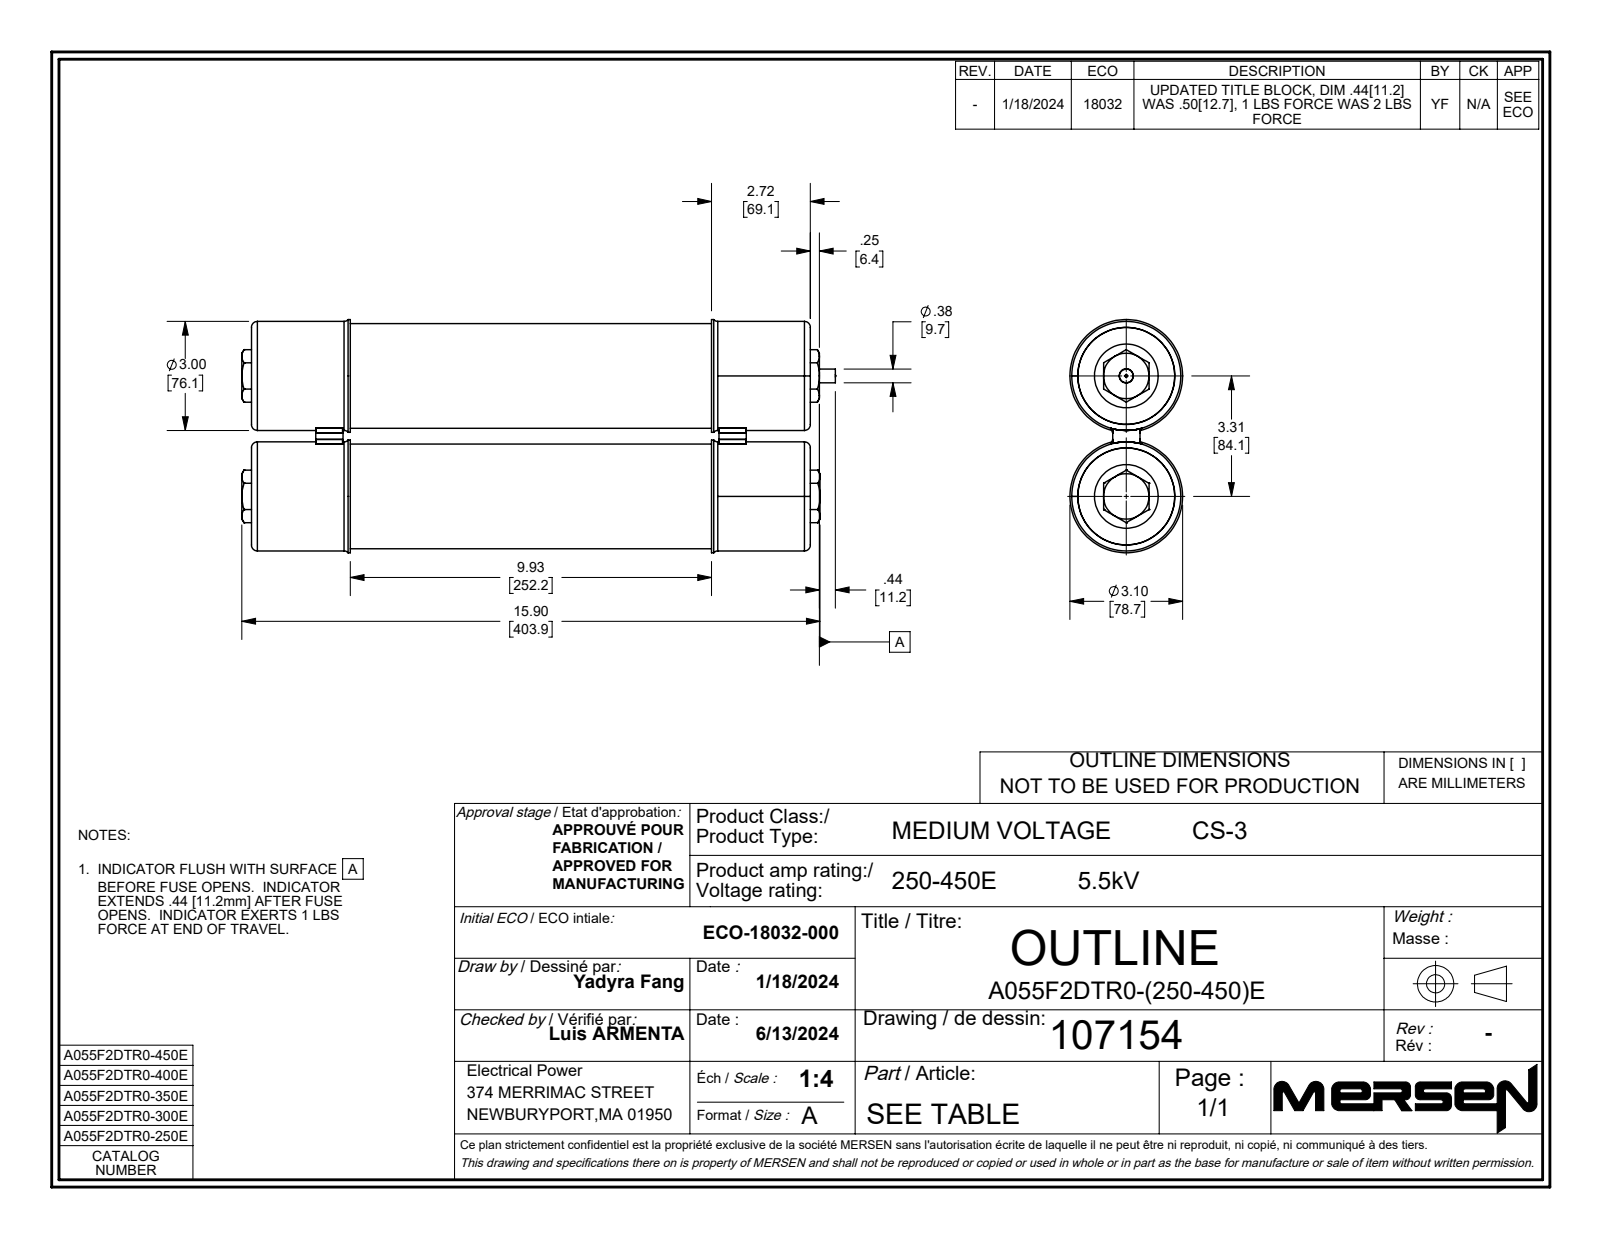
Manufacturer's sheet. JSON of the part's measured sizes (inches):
{"part_name": "360032; 130078_-003; 150E RTV SEALER^340012; 340012_-001 SET (+8 more)", "step_written_by": "SolidWorks 2021 (AUTOMOTIVE_DESIGN)", "units": "inches", "bodies": {"solids": 23, "faces": 459, "planar": 169, "cylindrical": 150, "other": 140}, "overall_size": [15.902, 6.412, 3.1], "volume_in3": 42.8, "surface_area_in2": 817.9, "round_holes": [[0.906, 2], [2.625, 2], [2.89, 2], [2.998, 2], [0.02, 1], [0.063, 1], [0.146, 1], [0.188, 1], [0.391, 1], [0.465, 1], [0.512, 1]], "round_bosses_or_shafts": [[3.1, 2], [2.875, 2], [1.25, 2], [0.78, 2], [0.9, 1], [0.875, 1], [0.874, 1], [0.562, 1]], "partial_cylinders_radius": [[0.032, 4], [0.187, 4], [1.5, 2]], "face_to_face_distances": [0.054, 15.192, 15.246, 15.574, 0.328, 0.382, 15.52, 15.138, 0.411, 15.489], "hole_center_spacings": [3.312]}
